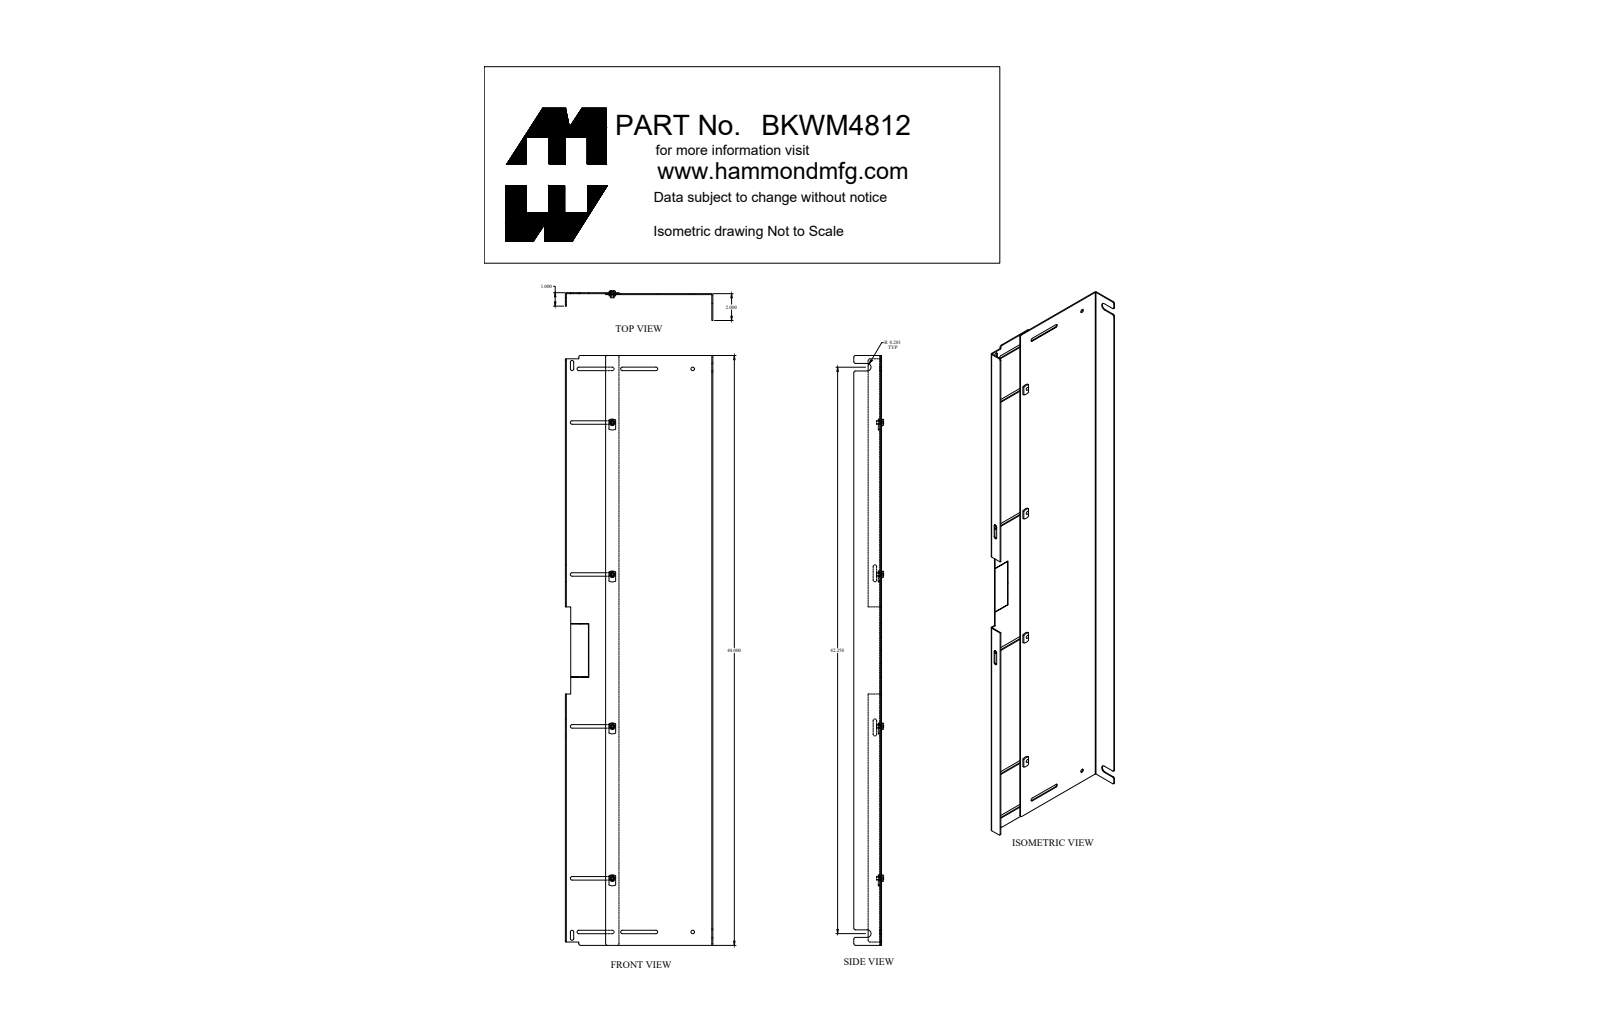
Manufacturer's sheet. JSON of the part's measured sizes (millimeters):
{"part_name": "BKWM4812_Default", "step_written_by": "SolidWorks 2019 (CONFIG_CONTROL_DESIGN)", "units": "millimeters", "bodies": {"solids": 10, "faces": 308, "planar": 156, "cylindrical": 108, "other": 44}, "overall_size": [1117.6, 255, 56.8], "volume_mm3": 751000, "surface_area_mm2": 834200, "round_holes": [[5.1, 4], [8, 4], [6.6, 2]], "round_bosses_or_shafts": [[11.9, 4], [7.4, 4], [6.4, 4]], "partial_cylinders_radius": [[3.3, 20], [3.2, 18], [12.7, 8], [0.9, 2], [2.7, 2], [7.1, 2]], "face_to_face_distances": [1.8, 3.7, 253.1, 251.3, 255, 101.6, 51.8, 49.9, 201.4, 203.2], "hole_center_spacings": [183.2, 287.9, 418.2, 575.7, 694.3, 977.2, 287.9, 863.6]}
